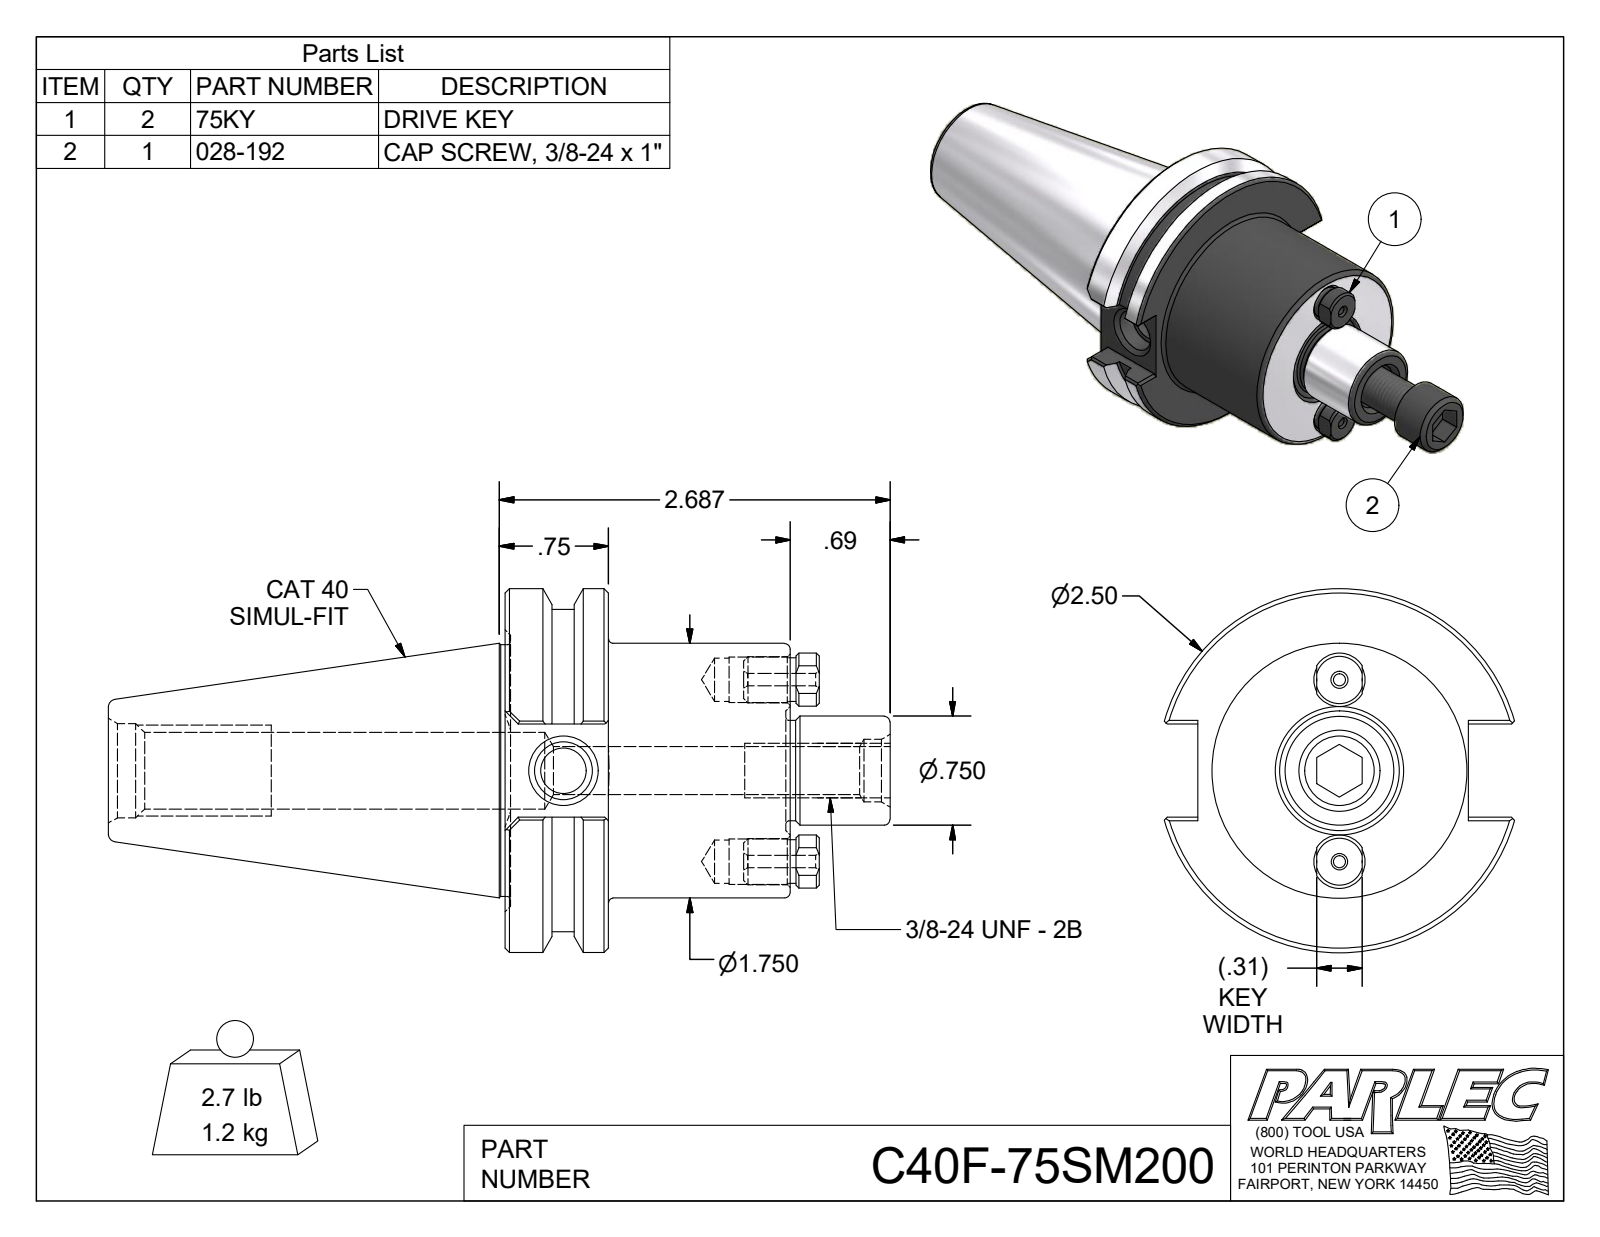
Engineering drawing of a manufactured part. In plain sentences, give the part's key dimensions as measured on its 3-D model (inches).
The part is named "C40F-75SM200; C40F-75SM2-1; 75KY; 028-192". Its 3-D file was written by "Autodesk Inventor 2018 (AUTOMOTIVE_DESIGN)". It is 4 solids with 138 faces: 57 planar, 31 cylindrical and 50 other. Overall it measures 6.206 by 2.5 by 2.406 inches. Its volume is 9.653 cubic inches and its surface area 47.21 square inches. Round holes: 2 of diameter 0.084, 2 of diameter 0.297, 2 of diameter 0.312, 1 of diameter 0.315, 1 of diameter 0.33, 1 of diameter 0.399, 1 of diameter 0.43, 1 of diameter 0.527, 1 of diameter 0.648. Round bosses or shafts: 2 of diameter 0.318, 2 of diameter 0.3, 1 of diameter 2.5, 1 of diameter 2.215, 1 of diameter 1.75, 1 of diameter 0.75, 1 of diameter 0.69, 1 of diameter 0.556. Partial cylindrical surfaces (rounded edges, fillets, slot ends): 2 of radius 0.182. The main face-to-face distances are 0.71, 1.96, 1.25, 1.86, 0.64, 2.727, 3.437, 4.687, 3.05, 0.323. The hole center spacings are 0.625, 1.25.
